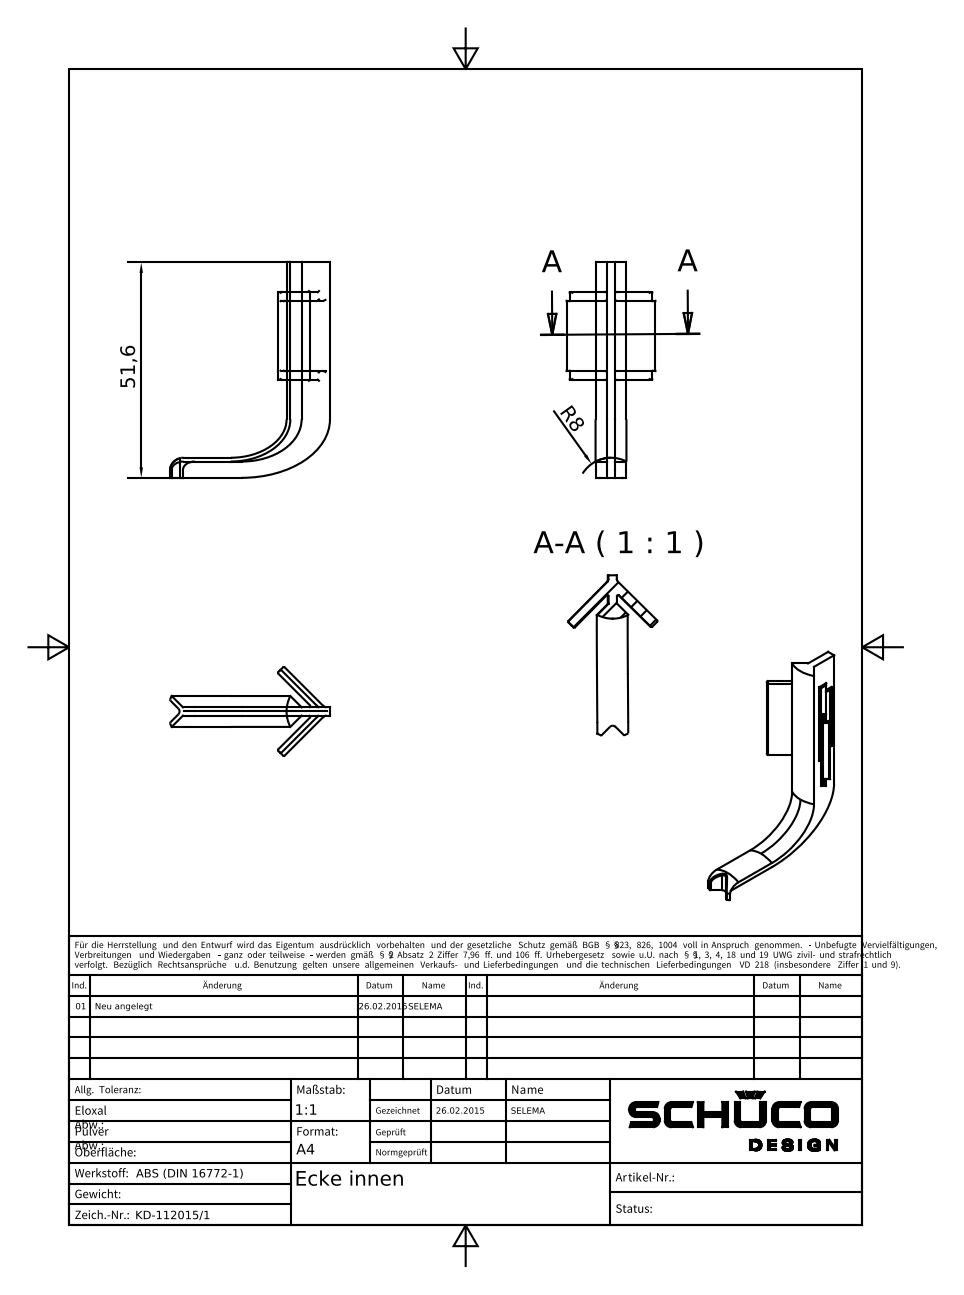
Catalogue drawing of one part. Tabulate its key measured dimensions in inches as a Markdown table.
| quantity | value |
| --- | --- |
| part name | KD-112015 |
| STEP written by | Autodesk Inventor 2024 (AUTOMOTIVE_DESIGN) |
| units | inches |
| bodies | 1 solid, 82 faces (31 planar, 42 cylindrical, 9 other) |
| overall size | 2.031 × 1.187 × 1.187 |
| volume | 0.174 in³ |
| surface area | 4.989 in² |
| partial cylindrical surfaces (radius × count) | 0.012 × 27, 0.039 × 3, 0.315 × 3, 0.079 × 2, 0.398 × 2 |
| main face-to-face distances | 0.085, 0.079, 0.154, 0.069, 0.112, 0.043, 0.041, 0.446, 0.515, 0.558 |
